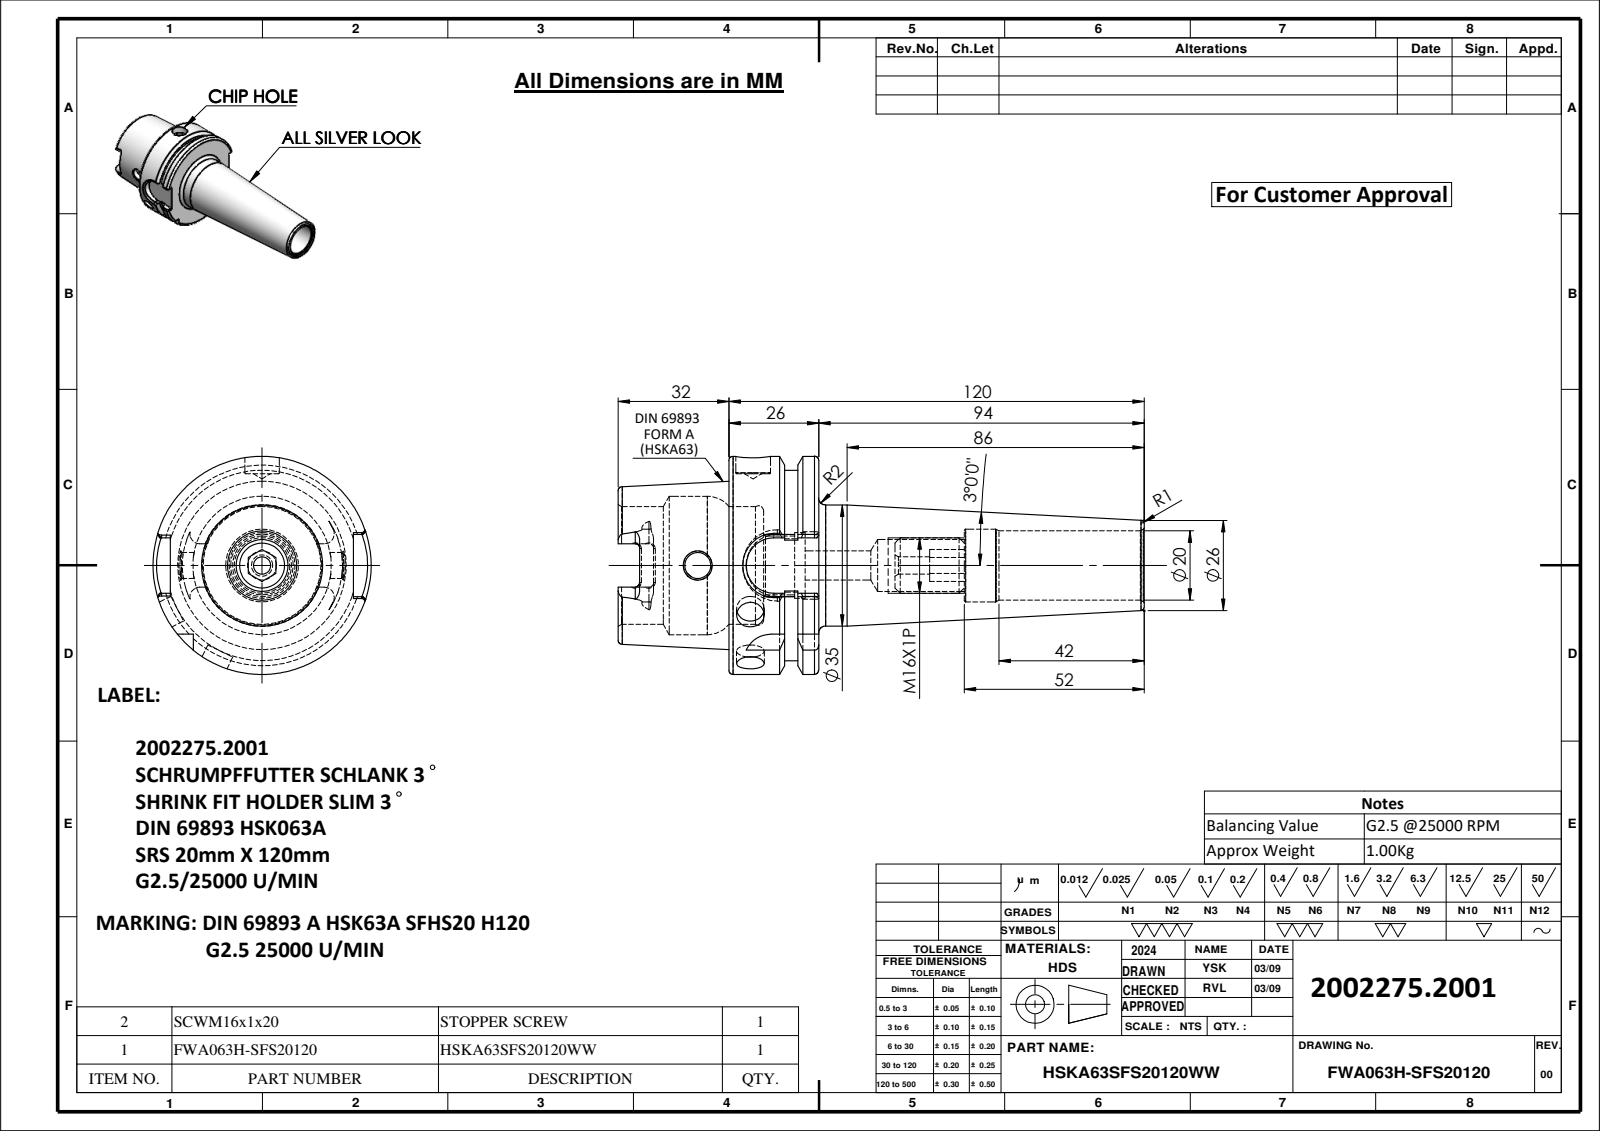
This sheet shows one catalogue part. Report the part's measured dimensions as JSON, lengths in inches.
{"part_name": "SCWM16X1P; HSKA63SFS20120WW; FWA063H-SFS20120", "step_written_by": "SolidWorks 2024 (CONFIG_CONTROL_DESIGN)", "units": "inches", "bodies": {"solids": 2, "faces": 196, "planar": 59, "cylindrical": 57, "other": 80}, "overall_size": [5.984, 2.48, 2.48], "volume_in3": 8.115, "surface_area_in2": 58.15, "round_holes": [[0.315, 2], [0.197, 1], [0.295, 1], [0.331, 1], [0.394, 1], [0.591, 1], [0.669, 1], [0.748, 1], [0.787, 1], [0.827, 1], [1.339, 1], [1.575, 1]], "round_bosses_or_shafts": [[2.48, 1], [2.165, 1], [1.378, 1], [0.63, 1]], "partial_cylinders_radius": [[0.051, 6], [0.113, 4], [0.315, 2], [0.354, 1]], "face_to_face_distances": [1.022, 0.394, 0.628, 1.26, 1.654, 2.281, 2.083, 2.283, 2.126, 0.866]}
